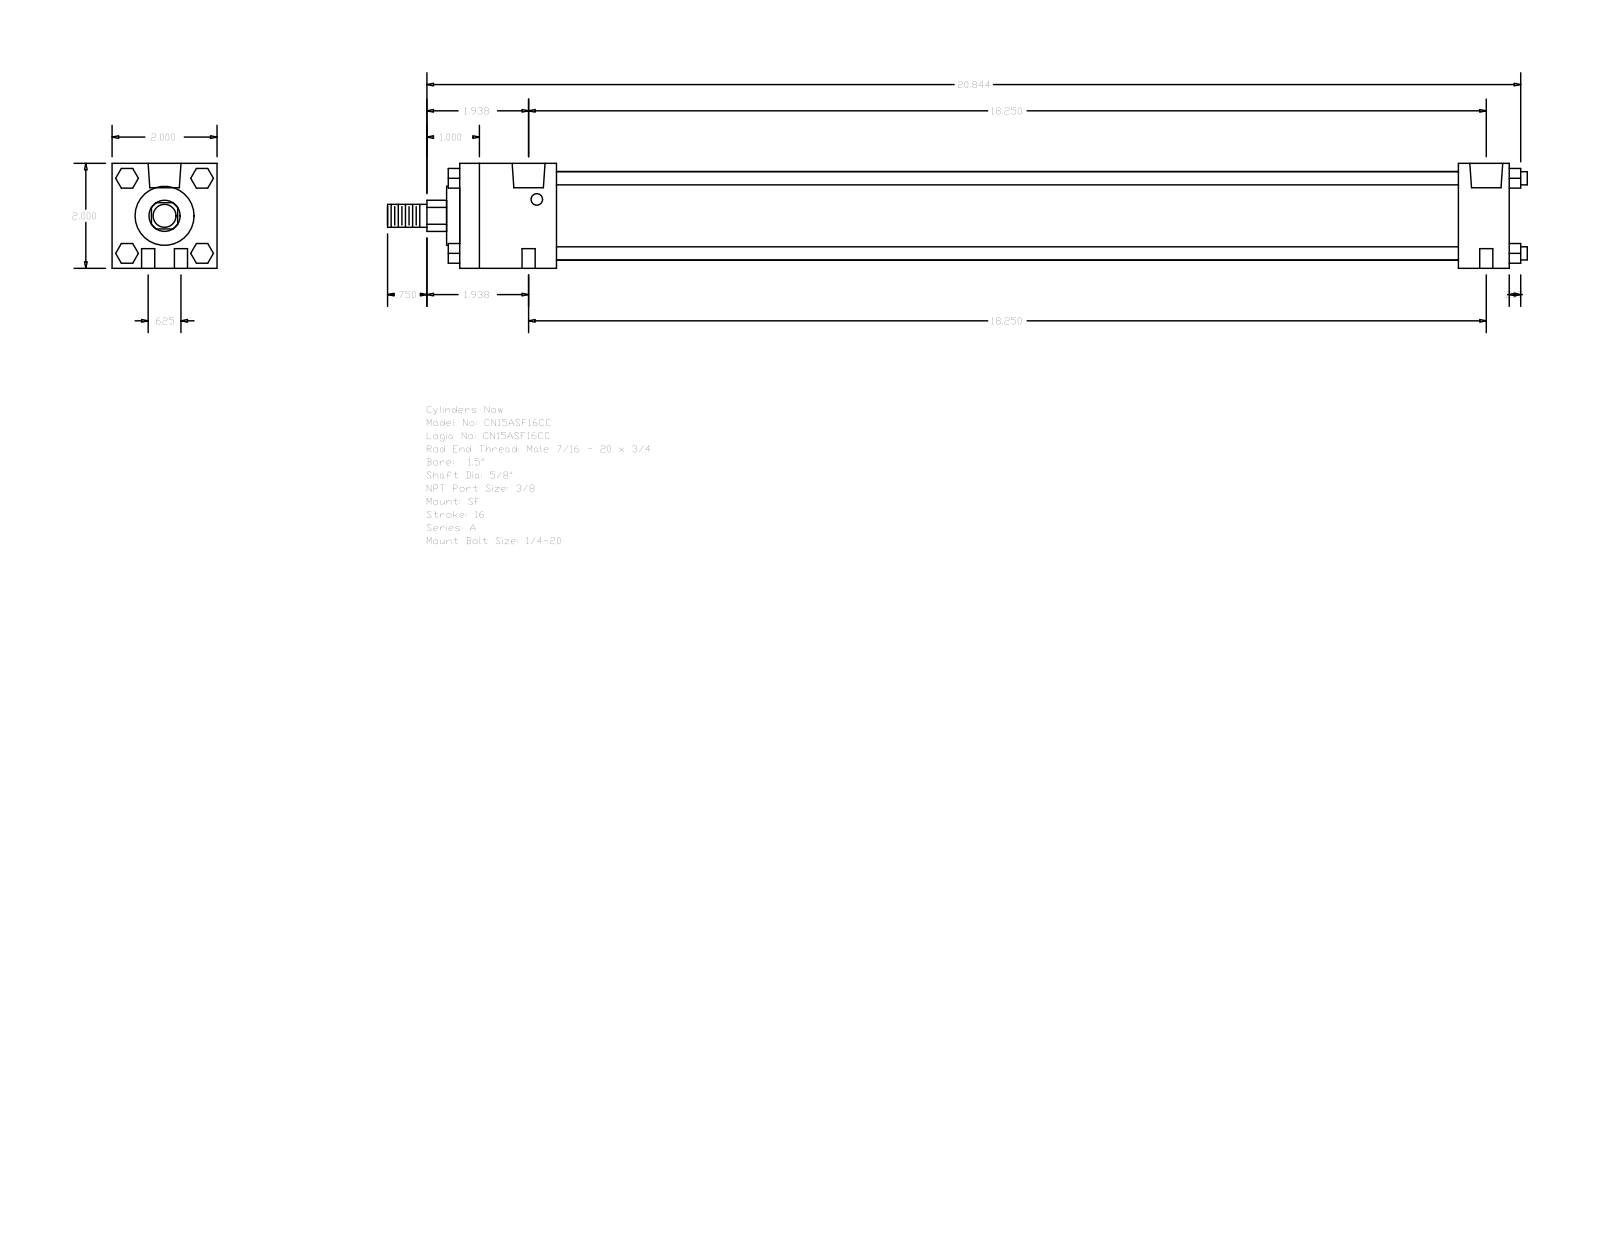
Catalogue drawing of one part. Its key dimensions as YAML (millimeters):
part_name: "A_SF__0150_0.625"
step_written_by: "GSSL Pune (CONFIG_CONTROL_DESIGN)"
units: millimeters
bodies: {solids: 0, faces: 124, planar: 94, cylindrical: 30, other: 0}
overall_size: [551.66, 50.8, 50.8]
round_holes:
  - {diameter: 6.35, count: 4}
  - {diameter: 5.56, count: 2}
  - {diameter: 15.93, count: 2}
round_bosses_or_shafts:
  - {diameter: 6.35, count: 4}
  - {diameter: 42.93, count: 1}
  - {diameter: 28.57, count: 1}
  - {diameter: 15.88, count: 1}
  - {diameter: 11.11, count: 1}
partial_cylinders:
  - {radius: 7.54, count: 1}
face_to_face_distances: [50.8, 508, 46.83, 483.39, 436.56, 461.17, 24.61, 6.35, 9.52, 53.18]
hole_center_spacings: [7.94, 463.62, 463.55, 15.88, 463.82, 455.61]
